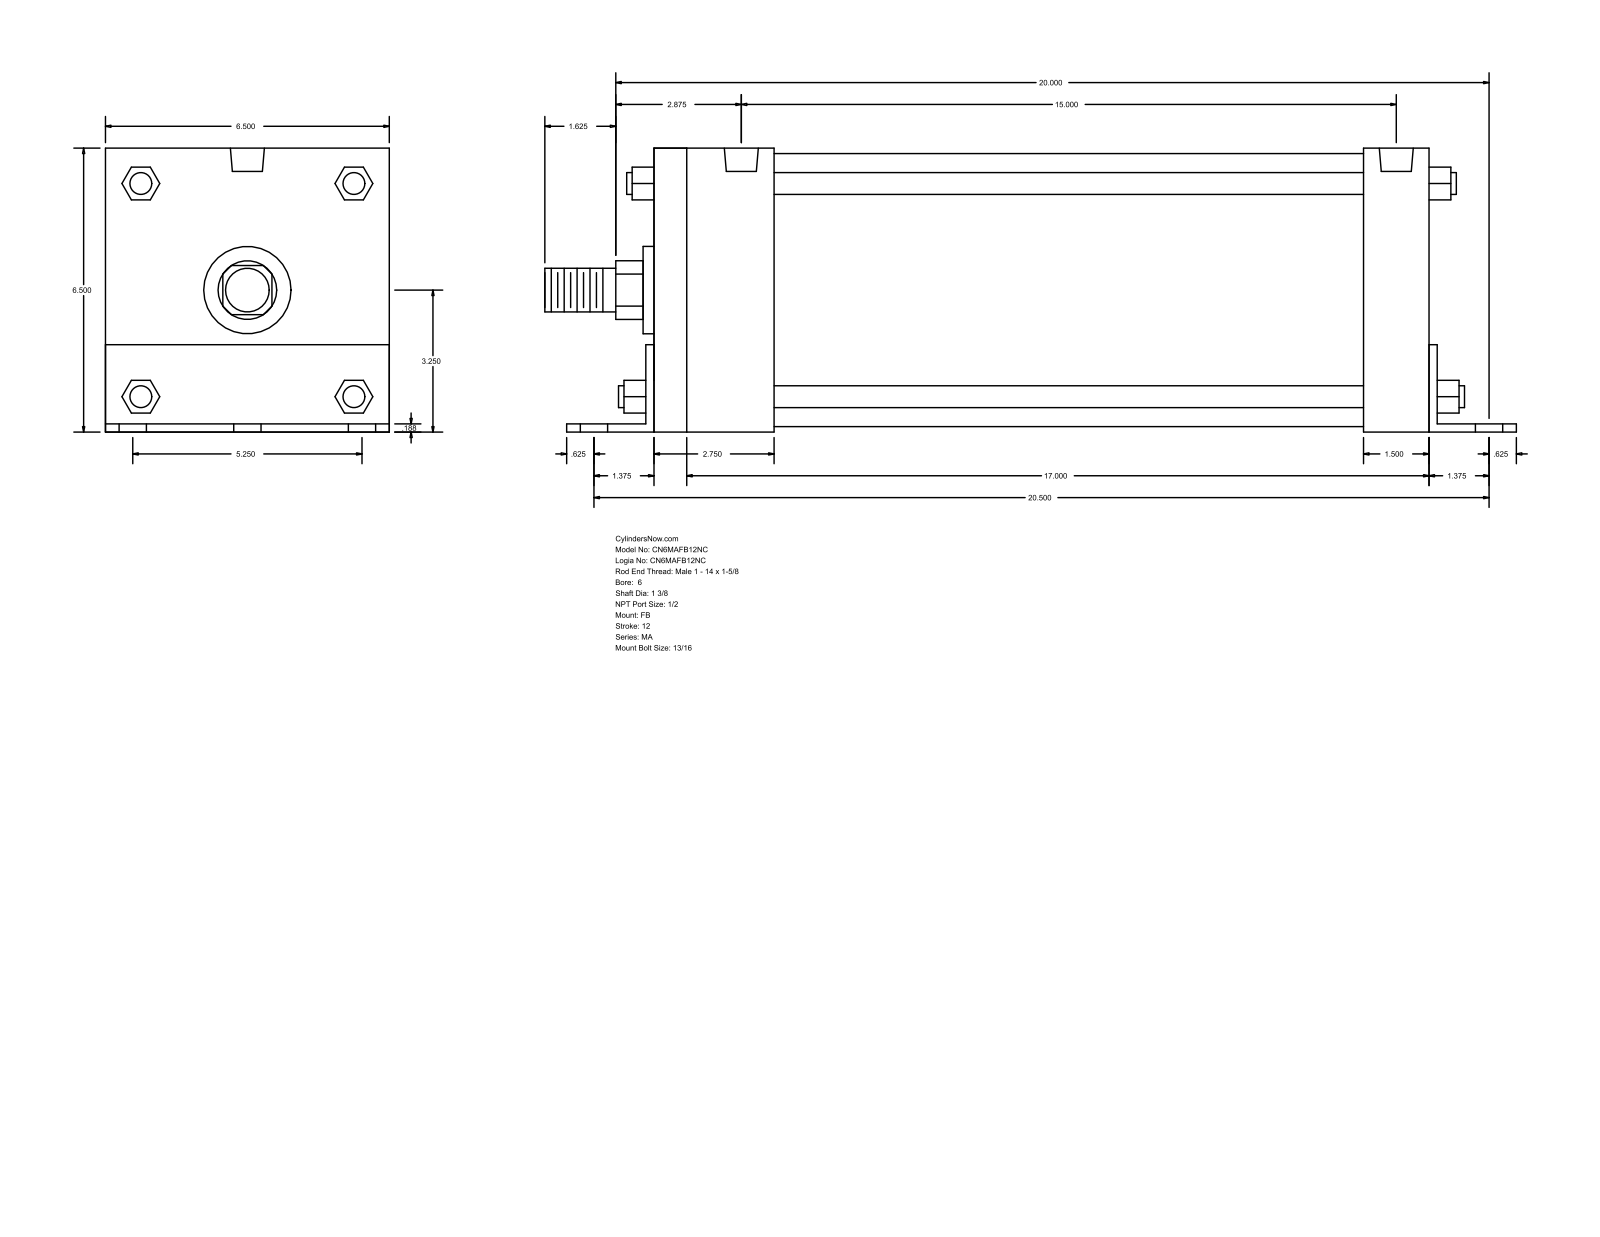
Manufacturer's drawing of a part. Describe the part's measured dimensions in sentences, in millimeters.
The part is named "MA_FB__0600_1.375". Its 3-D file was written by "GSSL Pune (CONFIG_CONTROL_DESIGN)". It is 0 solids with 140 faces: 105 planar, 35 cylindrical and 0 other. Overall it measures 561.98 by 165.15 by 165.1 millimeters. Round holes: 6 of diameter 20.64, 4 of diameter 17.46, 2 of diameter 19.77. Round bosses or shafts: 4 of diameter 12.7, 1 of diameter 158.75, 1 of diameter 50.8, 1 of diameter 34.92, 1 of diameter 25.4. Partial cylindrical surfaces (rounded edges, fillets, slot ends): 1 of radius 17.06, 1 of radius 32.05. The main face-to-face distances are 165.1, 4.76, 447.67, 165.15, 4.71, 160.39, 4.77, 38.1, 42.86, 457.2. The hole center spacings are 66.67, 521.8, 517.52, 83.82, 85.78, 108.6, 133.34, 377.82.
